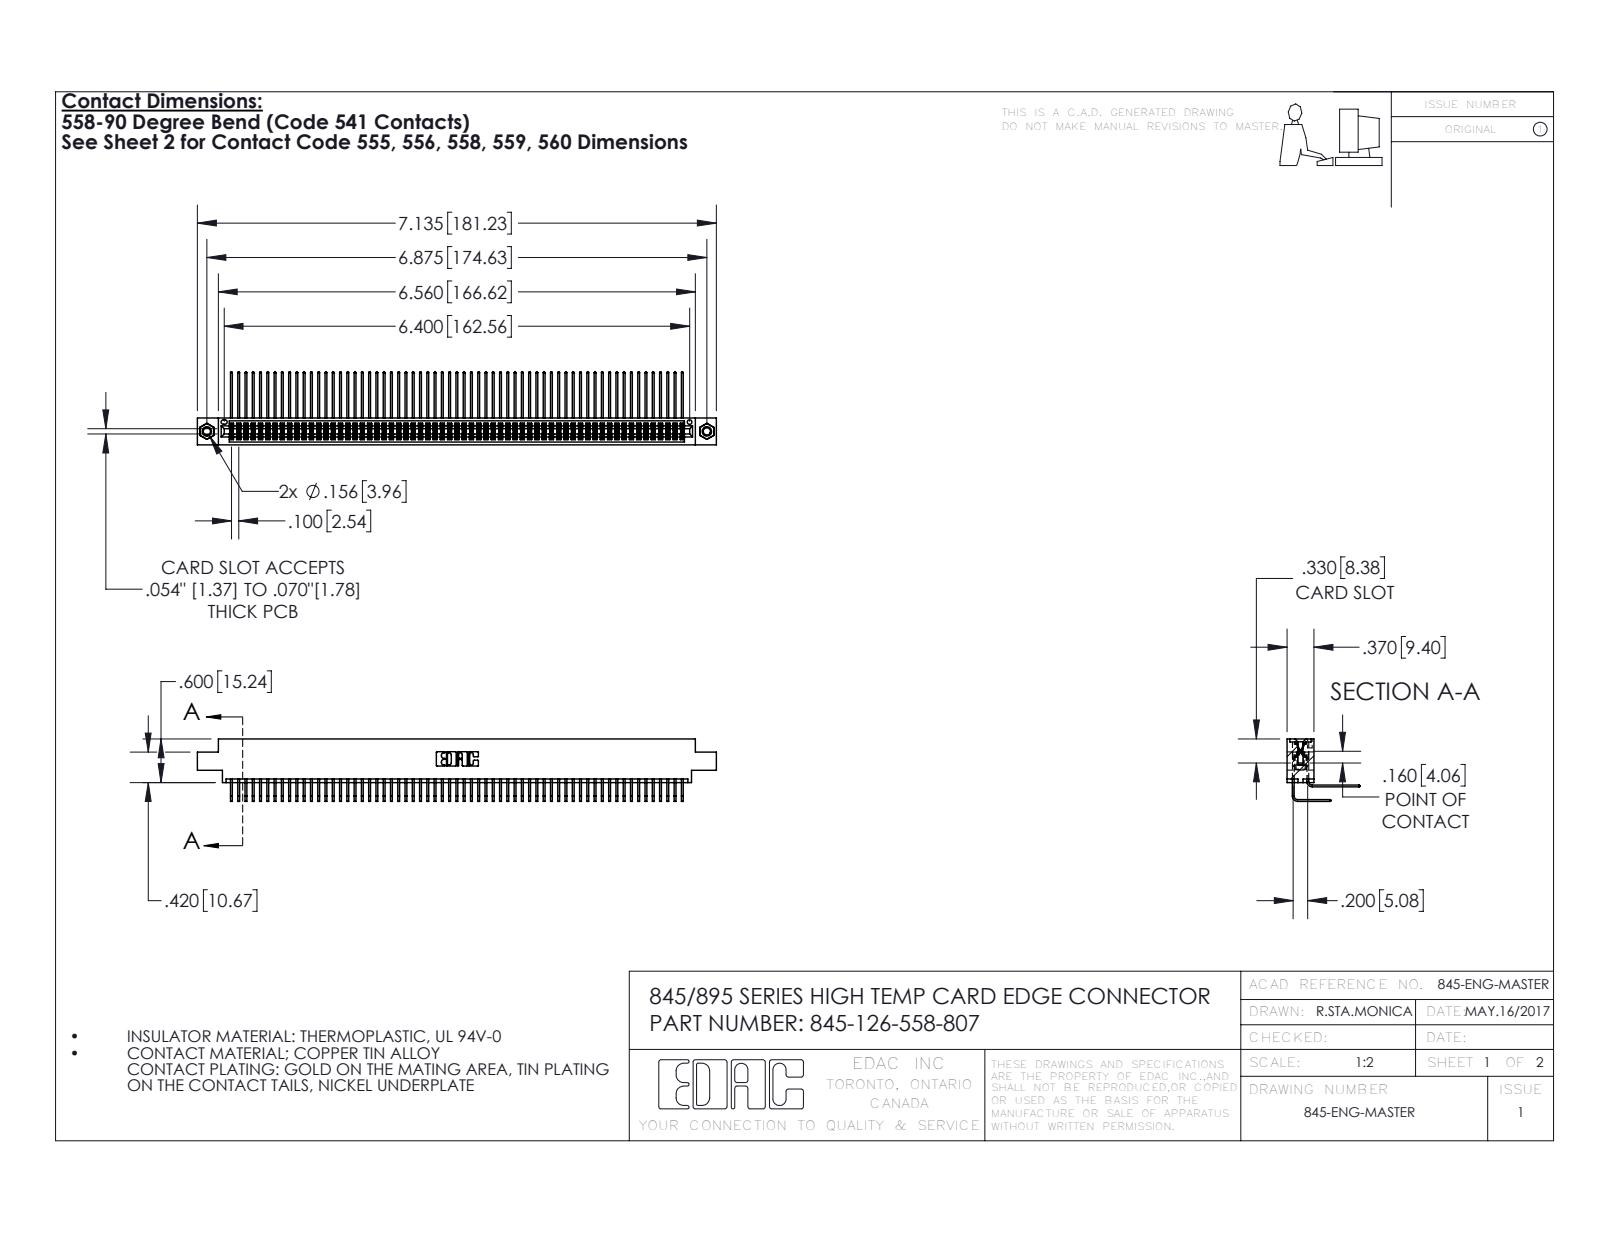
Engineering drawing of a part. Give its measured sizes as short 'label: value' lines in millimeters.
name: 345-292-001_558 Tail - 2; 345-250-001_345-250-005-103; 345 Part_0.170 Offset - 0.156 Dia-TI; 345-292-001_558 559 Tail - 1 (+1 more)
written by: SolidWorks 2016 (CONFIG_CONTROL_DESIGN)
unit: mm
bodies: 129 solids, 6742 faces (4526 planar, 2200 cylindrical, 16 other)
size: 181.2 × 25.5 × 21.8
volume: 18 400 mm³; area: 31 190 mm²
holes: 2× ⌀2.5, 2× ⌀3.2, 2× ⌀4, 1× ⌀1.6
bosses: 2× ⌀3.9
rounds: 190× R0.2, 22× R0.3, 6× R0.2, 6× R0.8, 3× R0.7, 2× R0.4, 2× R0.5, 2× R0.6
face distances: 1.8, 7.6, 5.1, 9.4, 2.5, 6.9, 0.6, 5.7, 4.4, 0.6
hole spacings: 6.9, 168.6, 174.6
